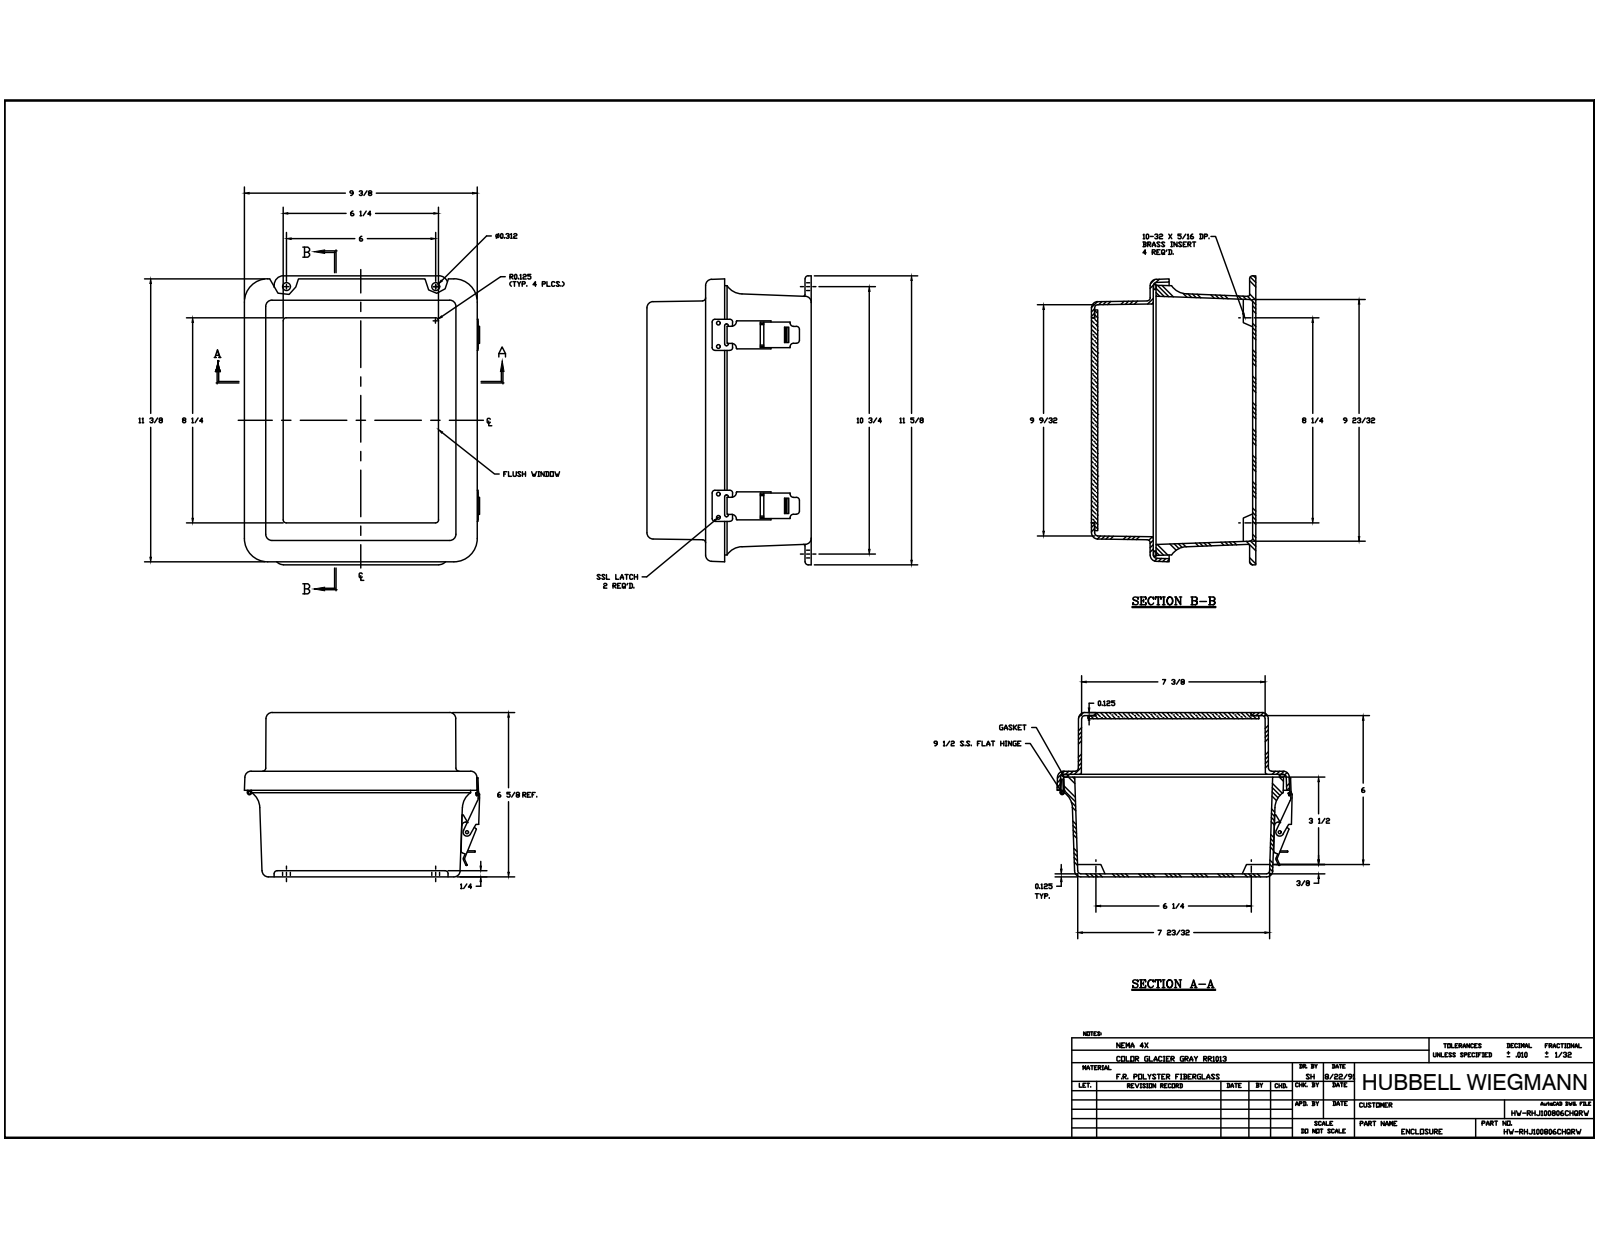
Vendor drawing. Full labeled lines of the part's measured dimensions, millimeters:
Part name (STEP PRODUCT): J1008HL_10; RMINS45821P_161; RMINS45821P_162; RMINS45821P_163 (+8 more)
STEP written by: Autodesk Inventor 2014 (AUTOMOTIVE_DESIGN)
Units: millimetres
Bodies: 39 solids, 1016 faces (424 planar, 421 cylindrical, 171 other)
Overall size (bounding box): 295.27 × 242.16 × 167.48
Volume: 1 257 000 mm³ · Surface area: 655 867 mm²
Round holes (diameter × count): ⌀3.56 ×20, ⌀2.64 ×8, ⌀3.33 ×8, ⌀3.86 ×5, ⌀3.3 ×4, ⌀3.96 ×4, ⌀5.54 ×4, ⌀3.43 ×2, ⌀9.52 ×2, ⌀2.16 ×1, ⌀2.16 ×1
Round bosses / shafts (diameter × count): ⌀3.17 ×16, ⌀6.35 ×8, ⌀6.86 ×4, ⌀7.62 ×1, ⌀4.31 ×1, ⌀3.94 ×1, ⌀3.05 ×1
Partial cylindrical surfaces — rounded edges, fillets, slot ends (radius × count): R3.17 ×36, R0.38 ×20, R0.79 ×20, R1.14 ×16, R6.35 ×16, R0.76 ×12, R0.57 ×9, R1.52 ×6
Main face-to-face distances: 3.17, 161.13, 6.35, 167.48, 164.31, 157.96, 104.36, 56.77, 3.18, 101.19
Hole centre spacings: 177.8, 178.82, 23.81, 152.4, 19.05, 76.2, 6.35, 19.04
